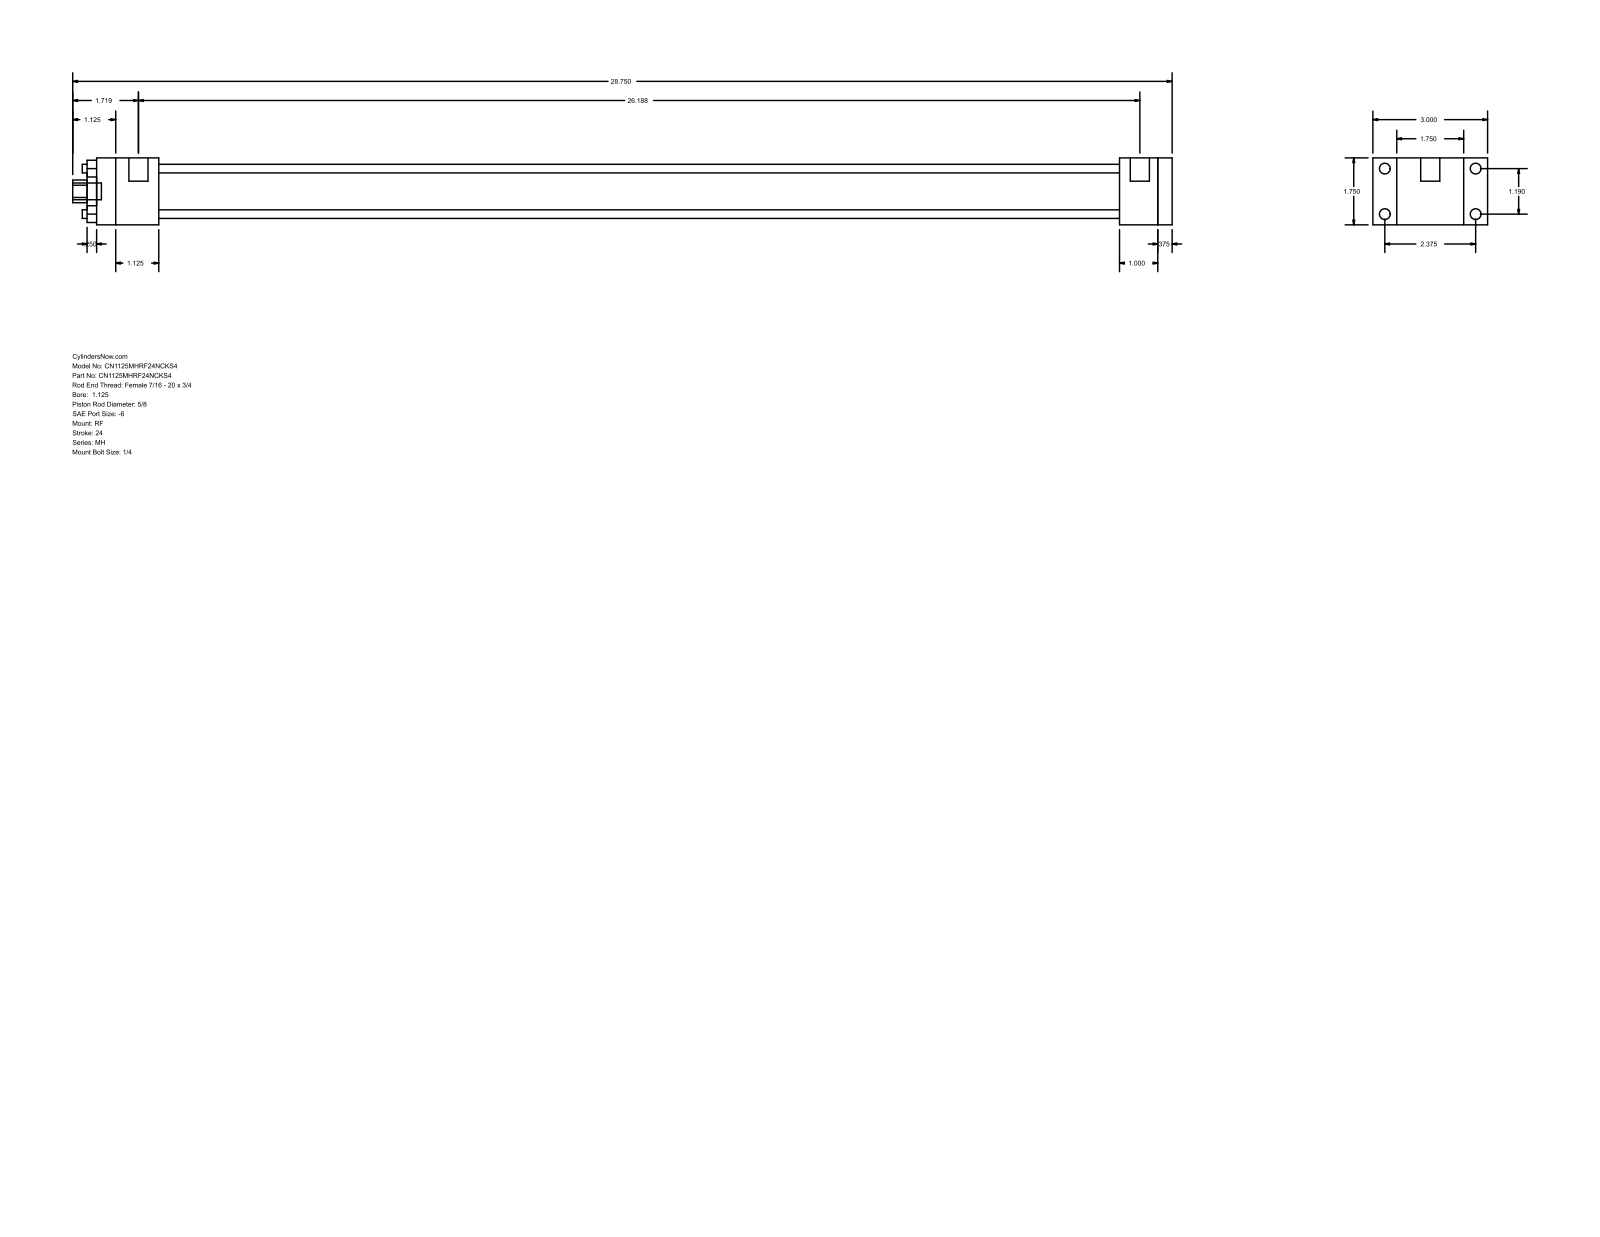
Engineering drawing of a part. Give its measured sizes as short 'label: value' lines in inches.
name: MH_RF__0112_0.625
written by: GSSL Pune (CONFIG_CONTROL_DESIGN)
unit: in
bodies: 0 solids, 92 faces (64 planar, 28 cylindrical, 0 other)
size: 28.75 × 3 × 1.75
holes: 4× ⌀0.225, 1× ⌀0.625, 1× ⌀1.125, 1× ⌀1.375
bosses: 4× ⌀0.281, 4× ⌀0.219, 2× ⌀0.5, 1× ⌀0.437
rounds: 1× R0.297
face distances: 1.75, 0.375, 0.625, 26.125, 26.5, 25.125, 1, 1.375, 1.625, 26.75
hole spacings: 0.841, 1.19, 1.683
